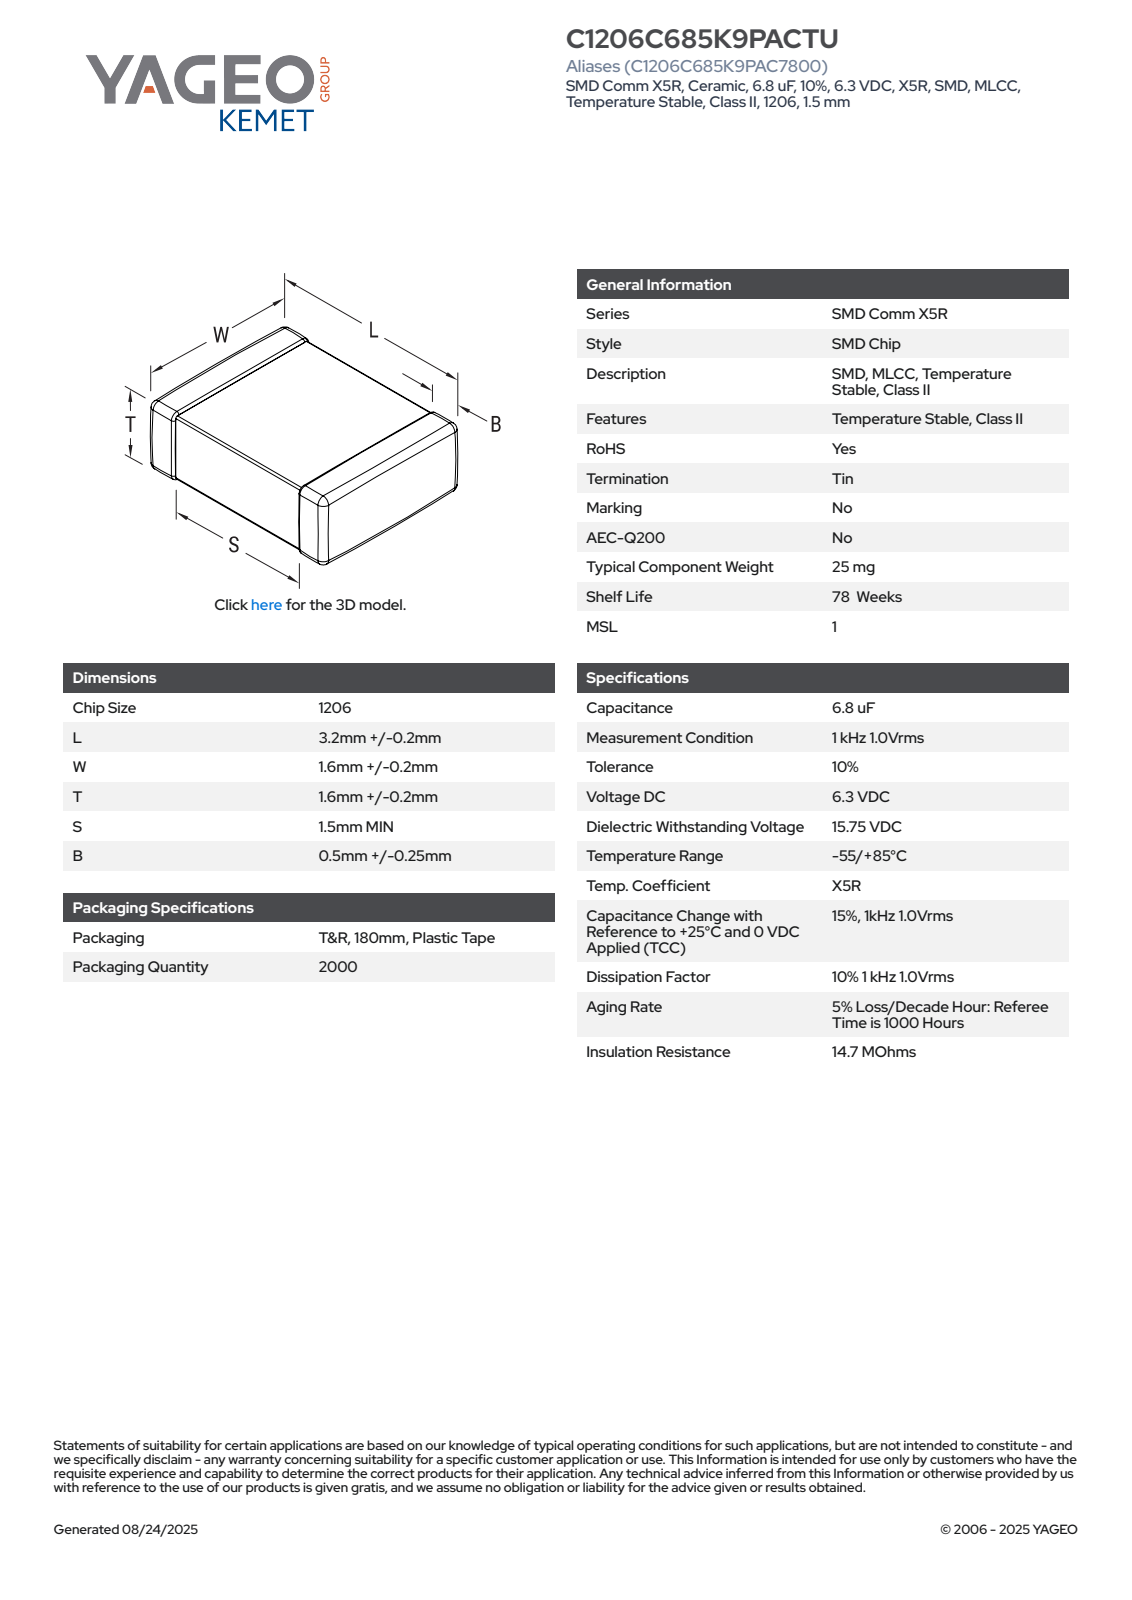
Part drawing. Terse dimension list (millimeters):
name: CCS_CCSTDNOS_1206_L3.4W1.8T0.9B0.75
written by: SolidWorks 2014 (AUTOMOTIVE_DESIGN)
unit: mm
bodies: 4 solids, 125 faces (71 planar, 38 cylindrical, 16 other)
size: 3.4 × 1.8 × 0.9
volume: 5 mm³; area: 21 mm²
face distances: 0.86, 0.82, 0.9, 1.76, 1.72, 3.4, 1.8, 0.87, 0.83, 0.99
